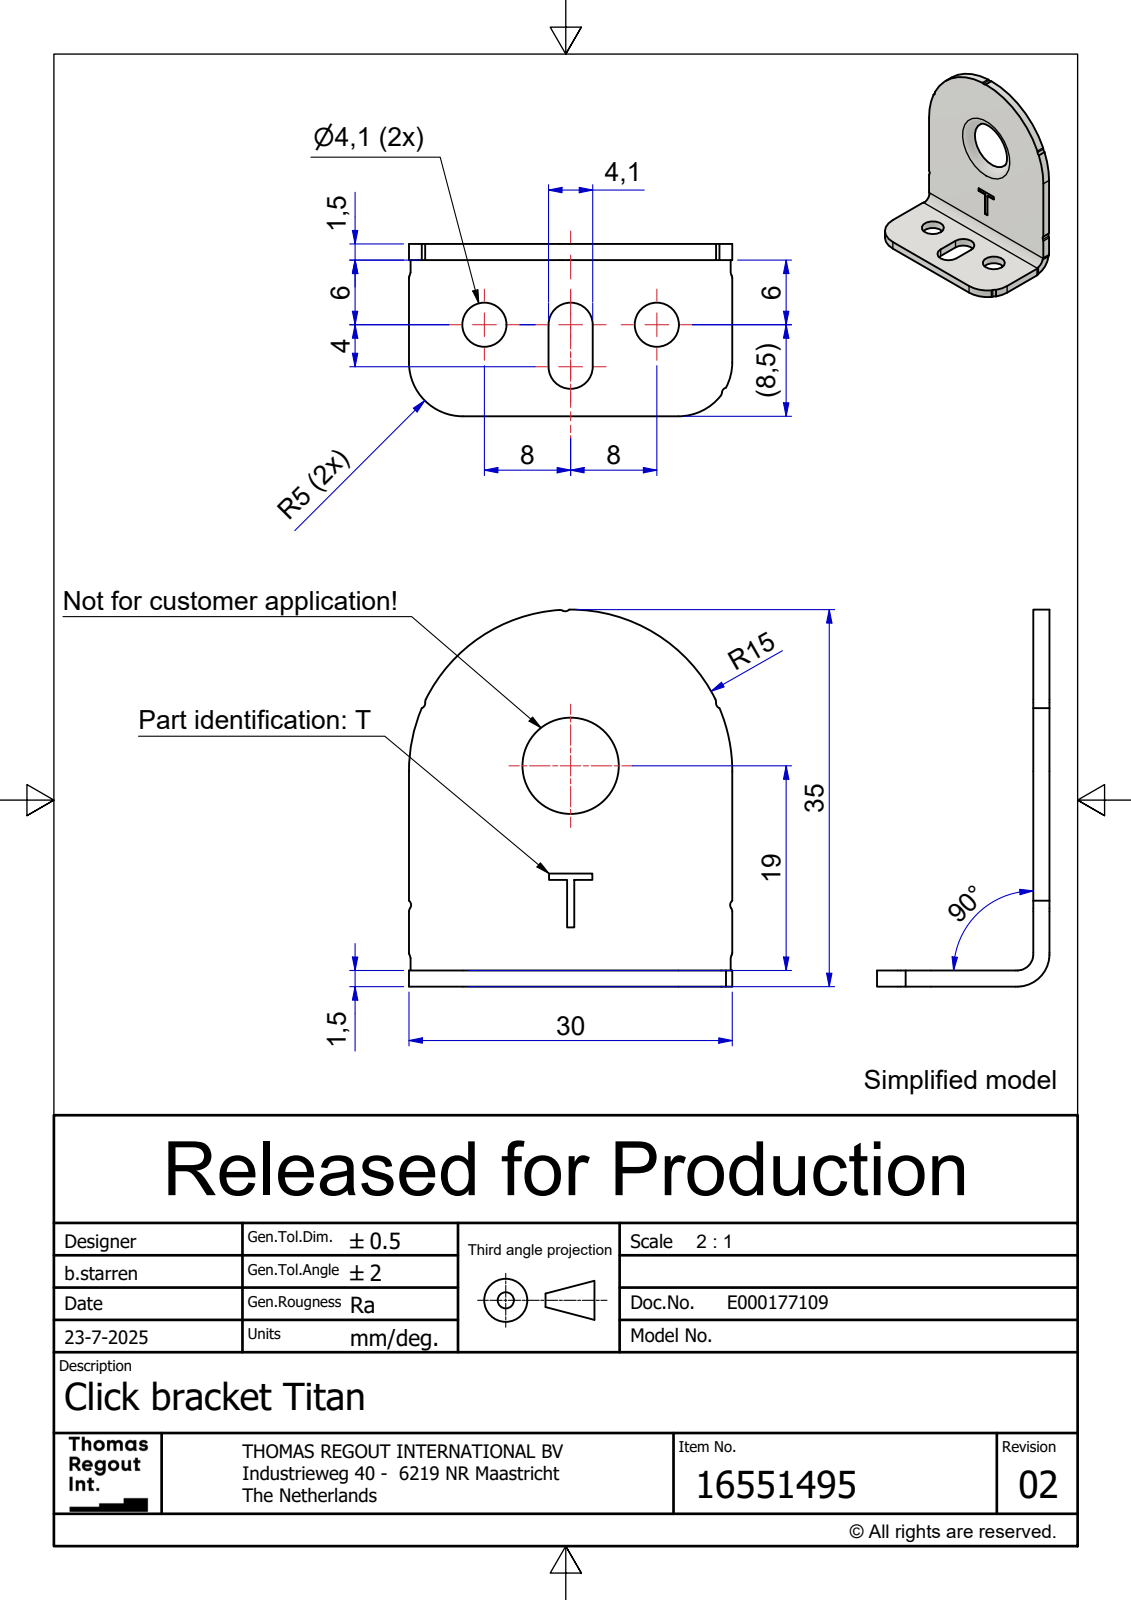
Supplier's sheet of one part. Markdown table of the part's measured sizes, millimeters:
| quantity | value |
| --- | --- |
| part name | E000173778 |
| STEP written by | Autodesk Inventor 2022 (AUTOMOTIVE_DESIGN) |
| units | millimeters |
| bodies | 1 solid, 58 faces (24 planar, 33 cylindrical, 1 other) |
| overall size | 35 × 30 × 16 |
| volume | 1 824 mm³ |
| surface area | 2 763 mm² |
| round holes (diameter × count) | 4.1 × 2 |
| partial cylindrical surfaces (radius × count) | 0.5 × 20, 2.05 × 2, 5 × 2, 1.5 × 1, 3 × 1, 15 × 1 |
| main face-to-face distances | 1.5, 30, 16, 14.5, 12.95, 17.05, 29.85, 12.8, 16.9, 4.1 |
| hole center spacings | 16 |
